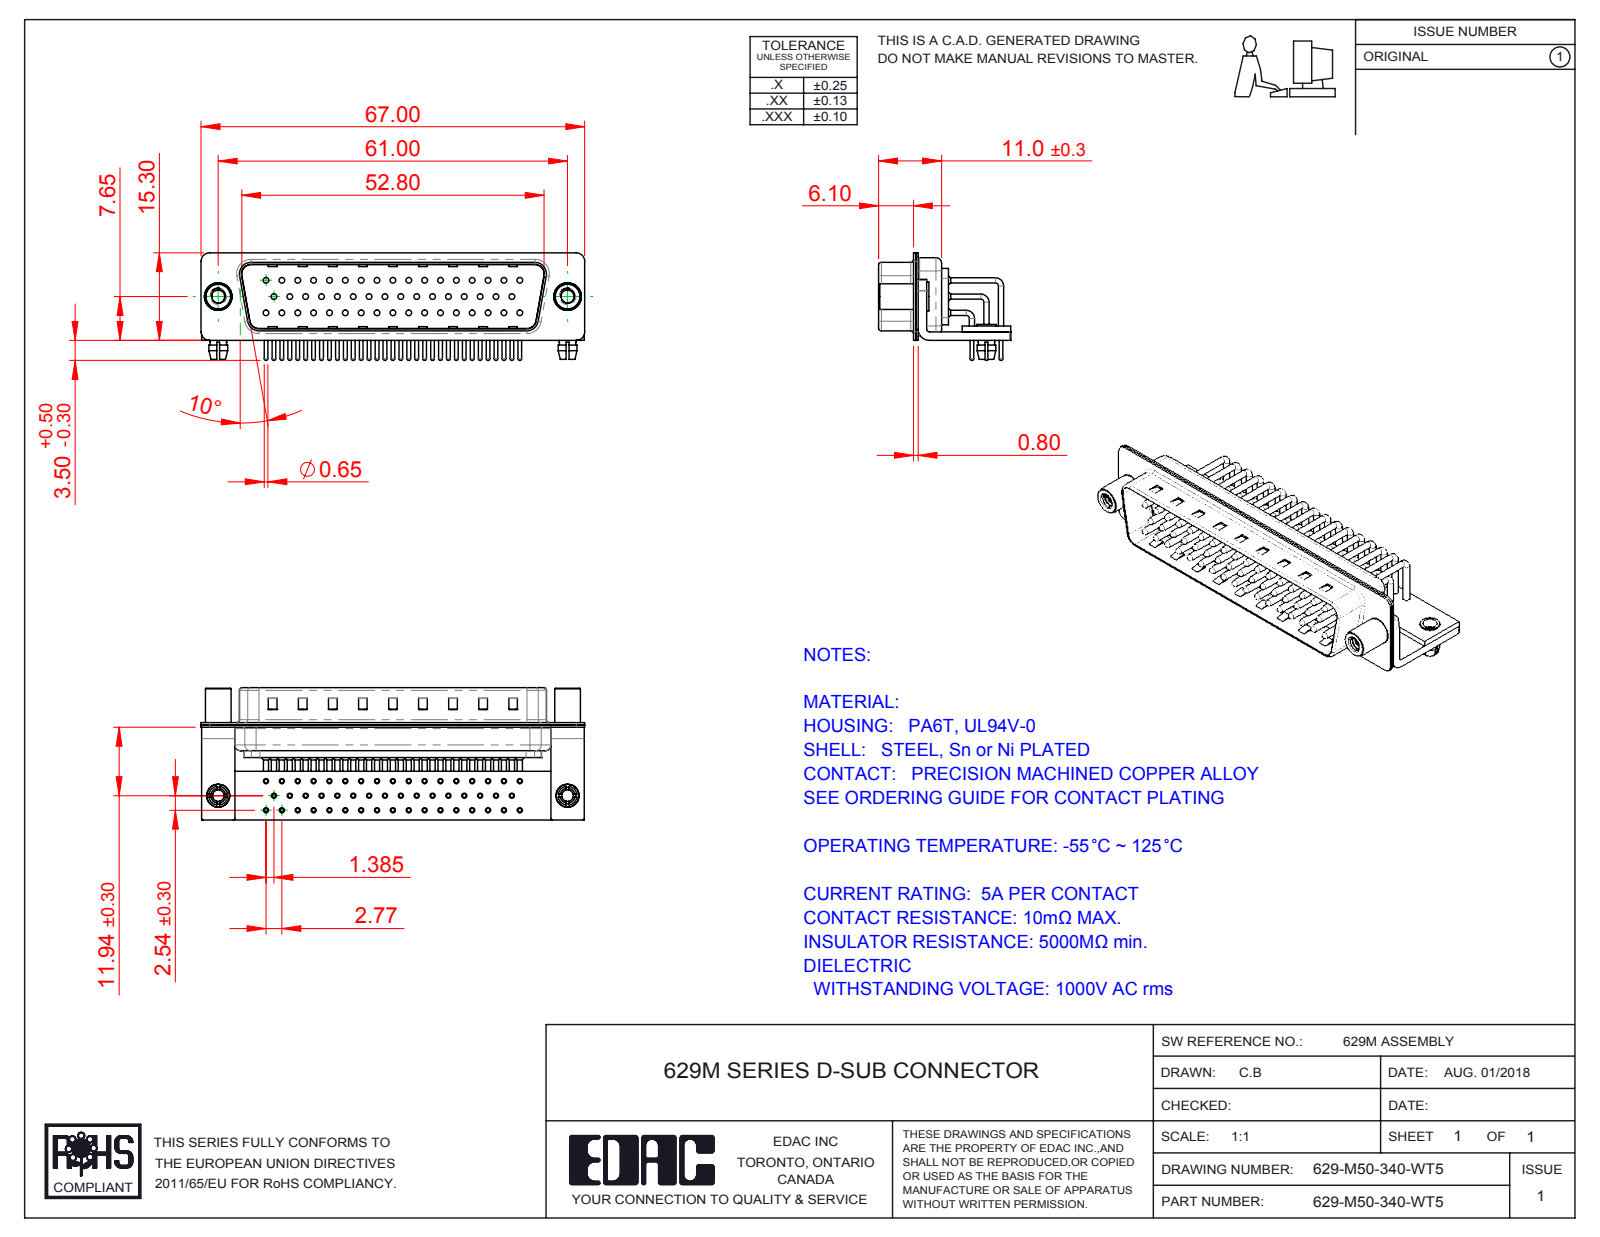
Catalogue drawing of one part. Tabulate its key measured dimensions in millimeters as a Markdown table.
| quantity | value |
| --- | --- |
| part name | 629M 4-40 Threaded Standoff; 629M Board Lock_50 Contacts; 629-M50-340-WT5; 629M Stabilizer Bracket_50 Contacts (+7 more) |
| STEP written by | SolidWorks 2016 (CONFIG_CONTROL_DESIGN) |
| units | millimeters |
| bodies | 60 solids, 6204 faces (3479 planar, 2137 cylindrical, 588 other) |
| overall size | 67 × 23.1 × 18.8 |
| volume | 6 007 mm³ |
| surface area | 15 495 mm² |
| round holes (diameter × count) | 2 × 52, 0.9 × 50, 1 × 50, 1.7 × 50, 2.26 × 2, 2.5 × 2, 3.2 × 2, 4 × 2, 4.8 × 2 |
| round bosses / shafts (diameter × count) | 0.9 × 58, 1.5 × 50, 0.65 × 50, 5 × 2, 4.9 × 2, 4.5 × 2, 4 × 2, 3.4 × 2 |
| partial cylindrical surfaces (radius × count) | 1.01 × 50, 0.25 × 16, 1.5 × 16, 2 × 13, 0.5 × 9, 1.6 × 8, 0.6 × 4, 0.65 × 4 |
| main face-to-face distances | 0.4, 1, 11.55, 1.5, 0.83, 5.7, 0.43, 11.95, 1.9, 0.8 |
| hole center spacings | 2.77, 5.54, 8.31, 11.08, 13.85, 16.62, 3.16, 19.39 |
